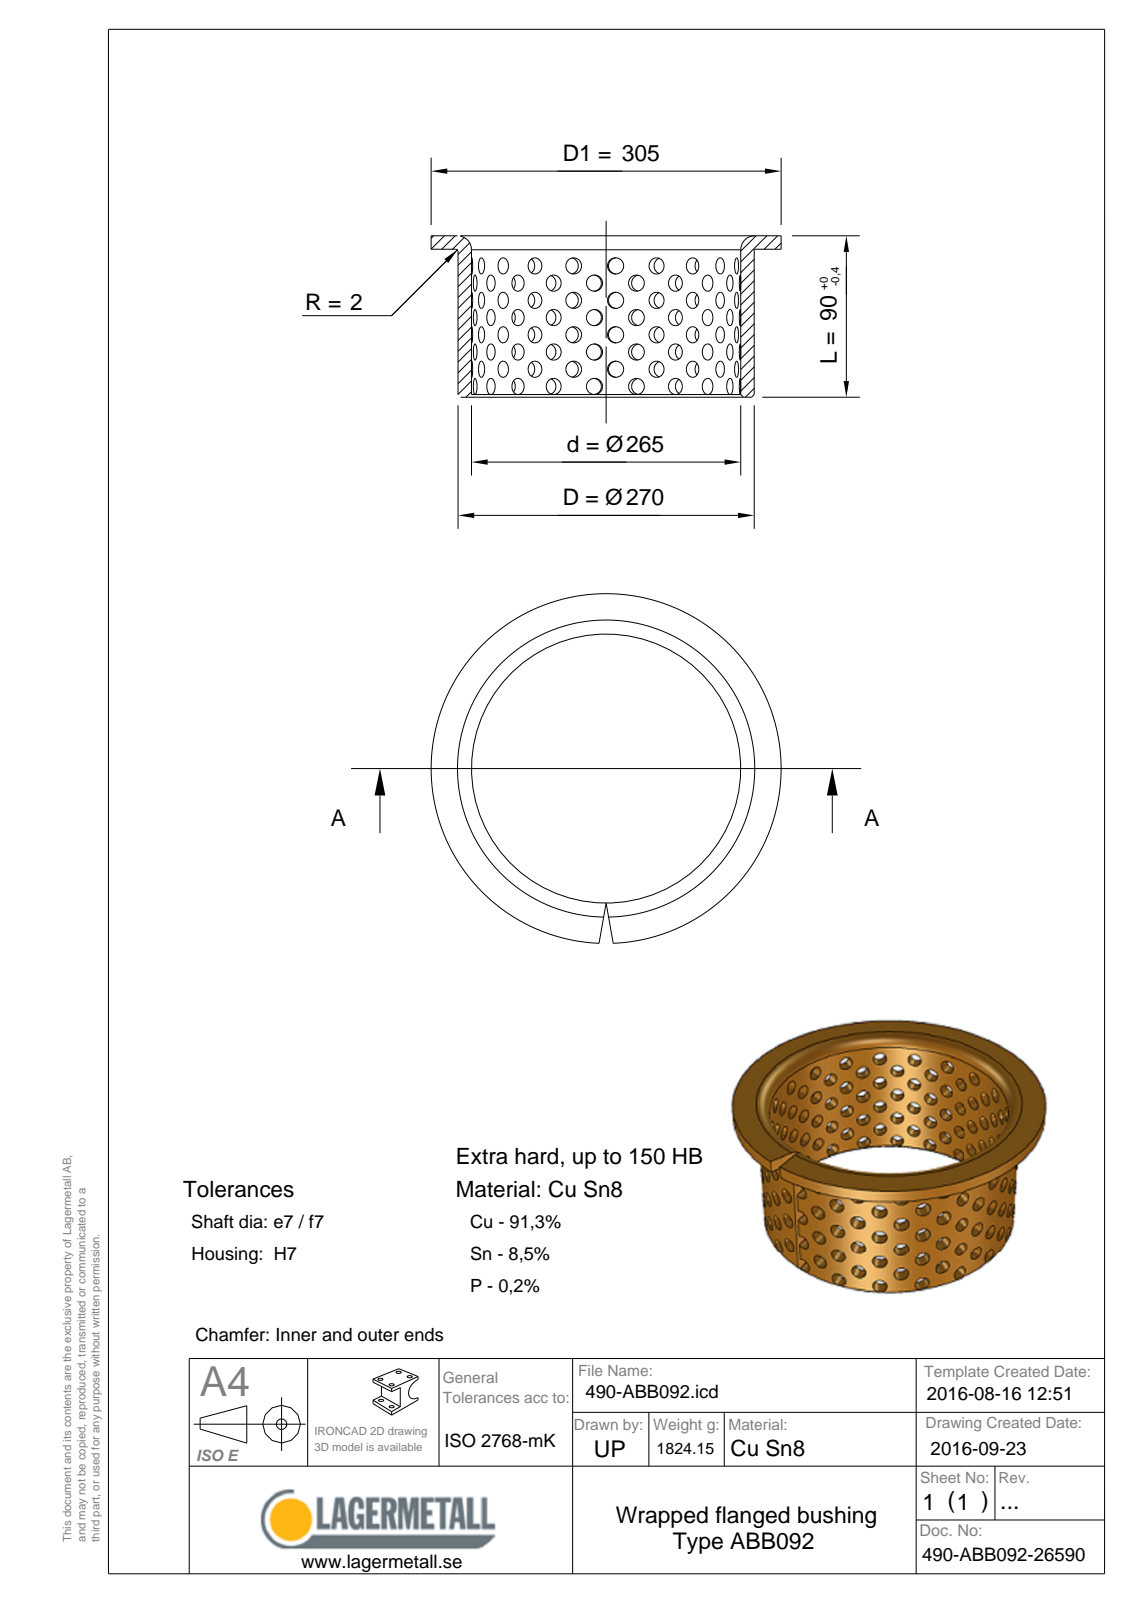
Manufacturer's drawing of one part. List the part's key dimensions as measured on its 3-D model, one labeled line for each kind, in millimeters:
STEP written by: Spatial InterOp 3D (CONFIG_CONTROL_DESIGN)
Units: millimetres
Bodies: 1 solid, 26 faces (5 planar, 9 cylindrical, 12 other)
Overall size (bounding box): 305 × 305 × 90
Volume: 225 203 mm³ · Surface area: 184 842 mm²
Round holes (diameter × count): ⌀265 ×1
Round bosses / shafts (diameter × count): ⌀305 ×1, ⌀270 ×1
Main face-to-face distances: 2.5, 87.5, 90
